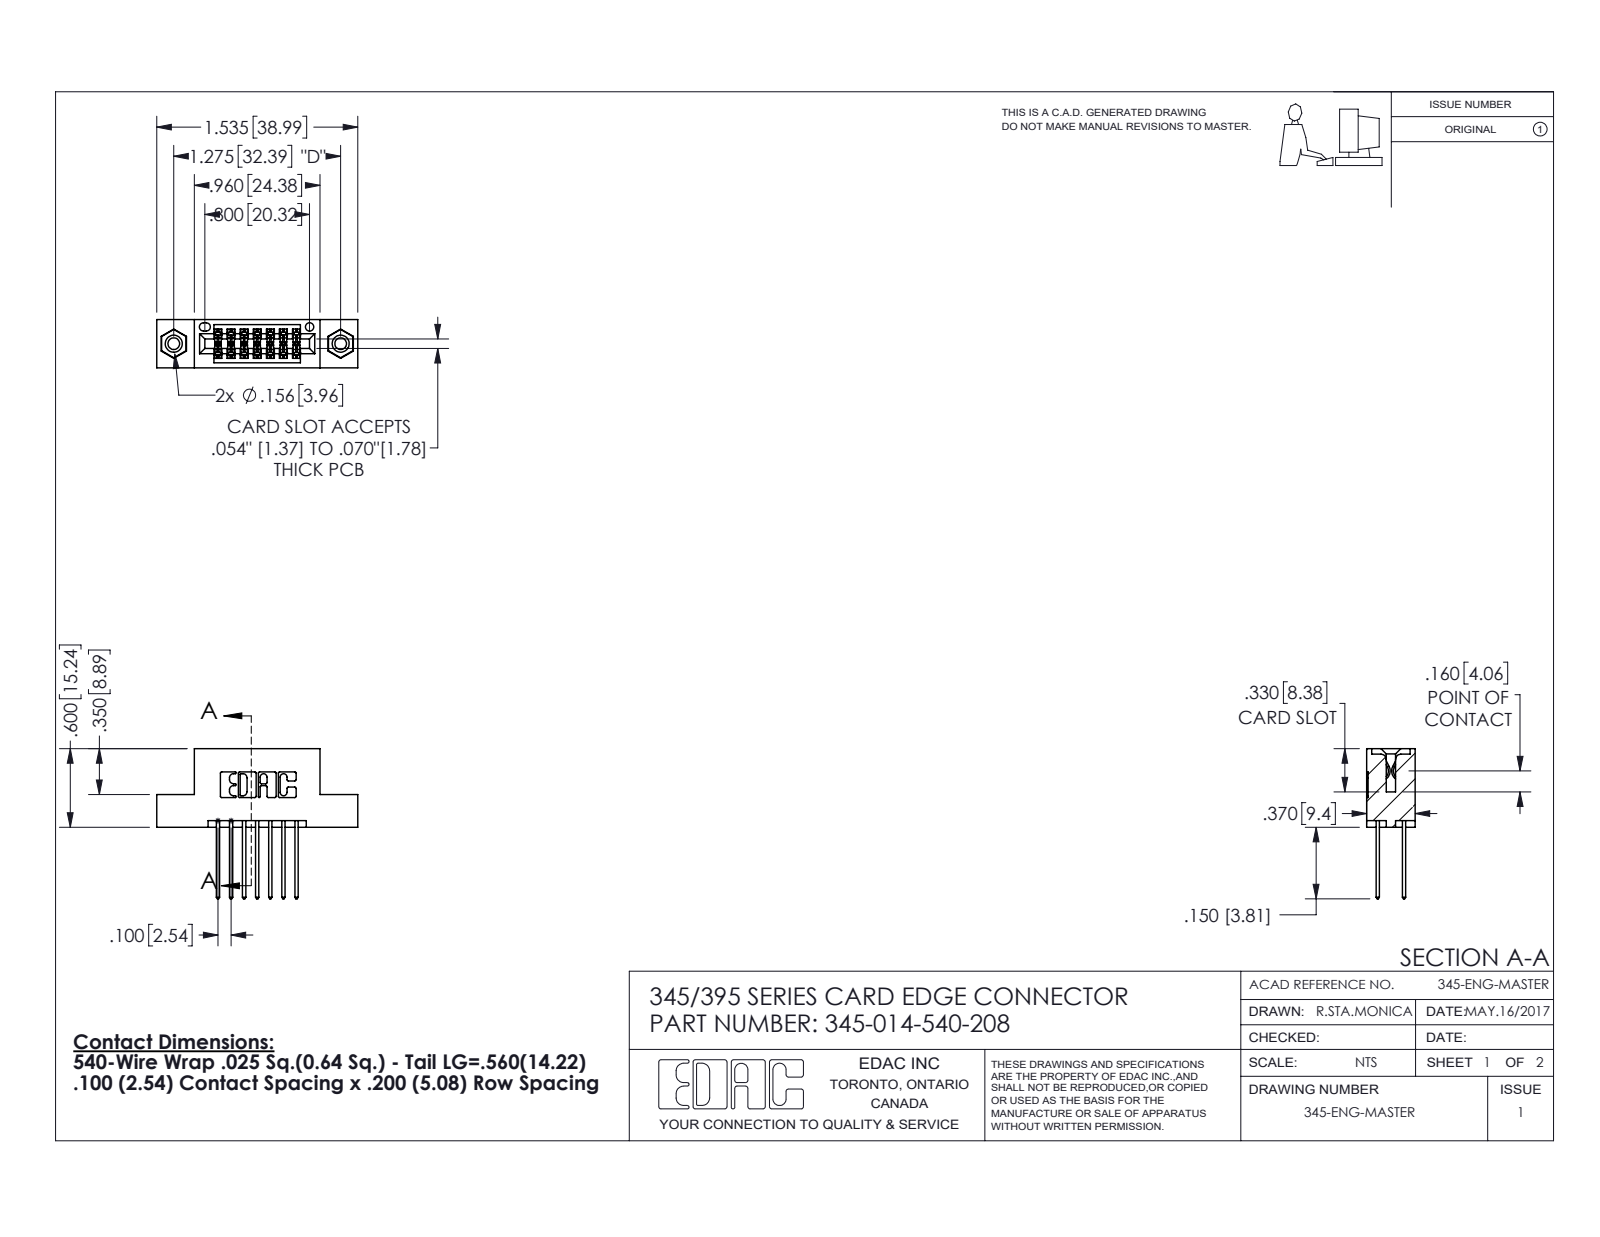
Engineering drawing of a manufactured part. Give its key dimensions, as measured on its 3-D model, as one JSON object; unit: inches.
{"part_name": "345-014-540-208; 345 Part_Flush Mounting Lugs - 0.156 Dia-TI; 345-250-001_345-250-003-102; 345-292-001_345-293-140", "step_written_by": "SolidWorks 2016 (CONFIG_CONTROL_DESIGN)", "units": "inches", "bodies": {"solids": 17, "faces": 886, "planar": 574, "cylindrical": 296, "other": 16}, "overall_size": [1.535, 1.147, 0.37], "volume_in3": 0.214, "surface_area_in2": 7.392, "round_holes": [[0.089, 2], [0.125, 2], [0.156, 2], [0.064, 1]], "round_bosses_or_shafts": [[0.155, 2]], "partial_cylinders_radius": [[0.01, 22], [0.006, 21], [0.01, 14], [0.007, 6], [0.031, 6], [0.026, 3], [0.014, 2], [0.019, 2]], "face_to_face_distances": [0.2, 0.072, 0.298, 0.37, 0.1, 0.098, 0.272, 0.025, 0.225, 0.3], "hole_center_spacings": [0.27, 1.045, 1.275]}
